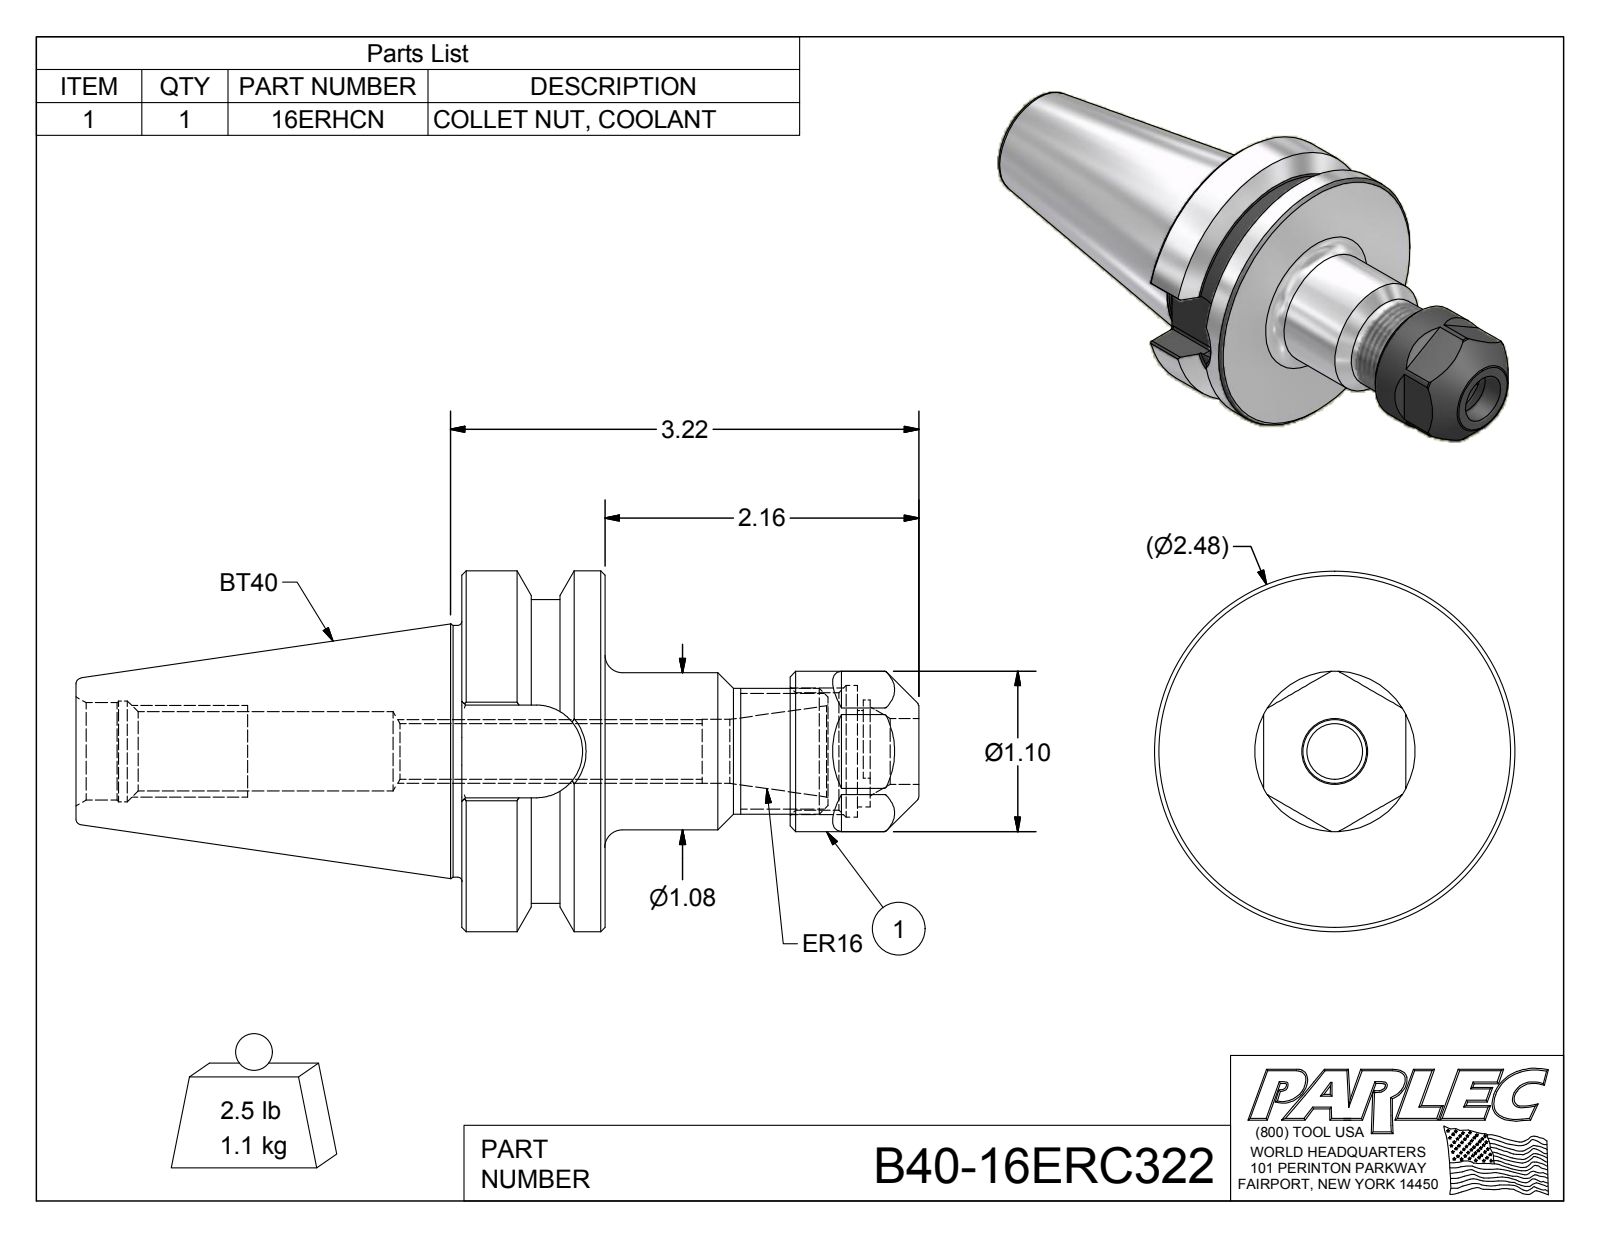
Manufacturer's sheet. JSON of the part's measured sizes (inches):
{"part_name": "B40-16ERC322; B40-16ER3-1; 16ERHCN", "step_written_by": "Autodesk Inventor 2012 (AUTOMOTIVE_DESIGN)", "units": "inches", "bodies": {"solids": 2, "faces": 106, "planar": 41, "cylindrical": 29, "other": 36}, "overall_size": [5.795, 2.48, 2.48], "volume_in3": 8.746, "surface_area_in2": 46.39, "round_holes": [[0.383, 1], [0.44, 1], [0.453, 1], [0.545, 1], [0.661, 1], [0.67, 1], [0.694, 1], [0.807, 1], [0.906, 1]], "round_bosses_or_shafts": [[2.48, 1], [2.087, 1], [1.73, 1], [1.102, 1], [1.08, 1], [0.866, 1]], "partial_cylinders_radius": [[0.02, 8], [0.319, 1], [0.354, 1]], "face_to_face_distances": [0.984, 0.979, 1.78, 0.401, 1.38, 2.721, 1.737, 2.653, 3.637, 5.374], "hole_center_spacings": [0.051]}
